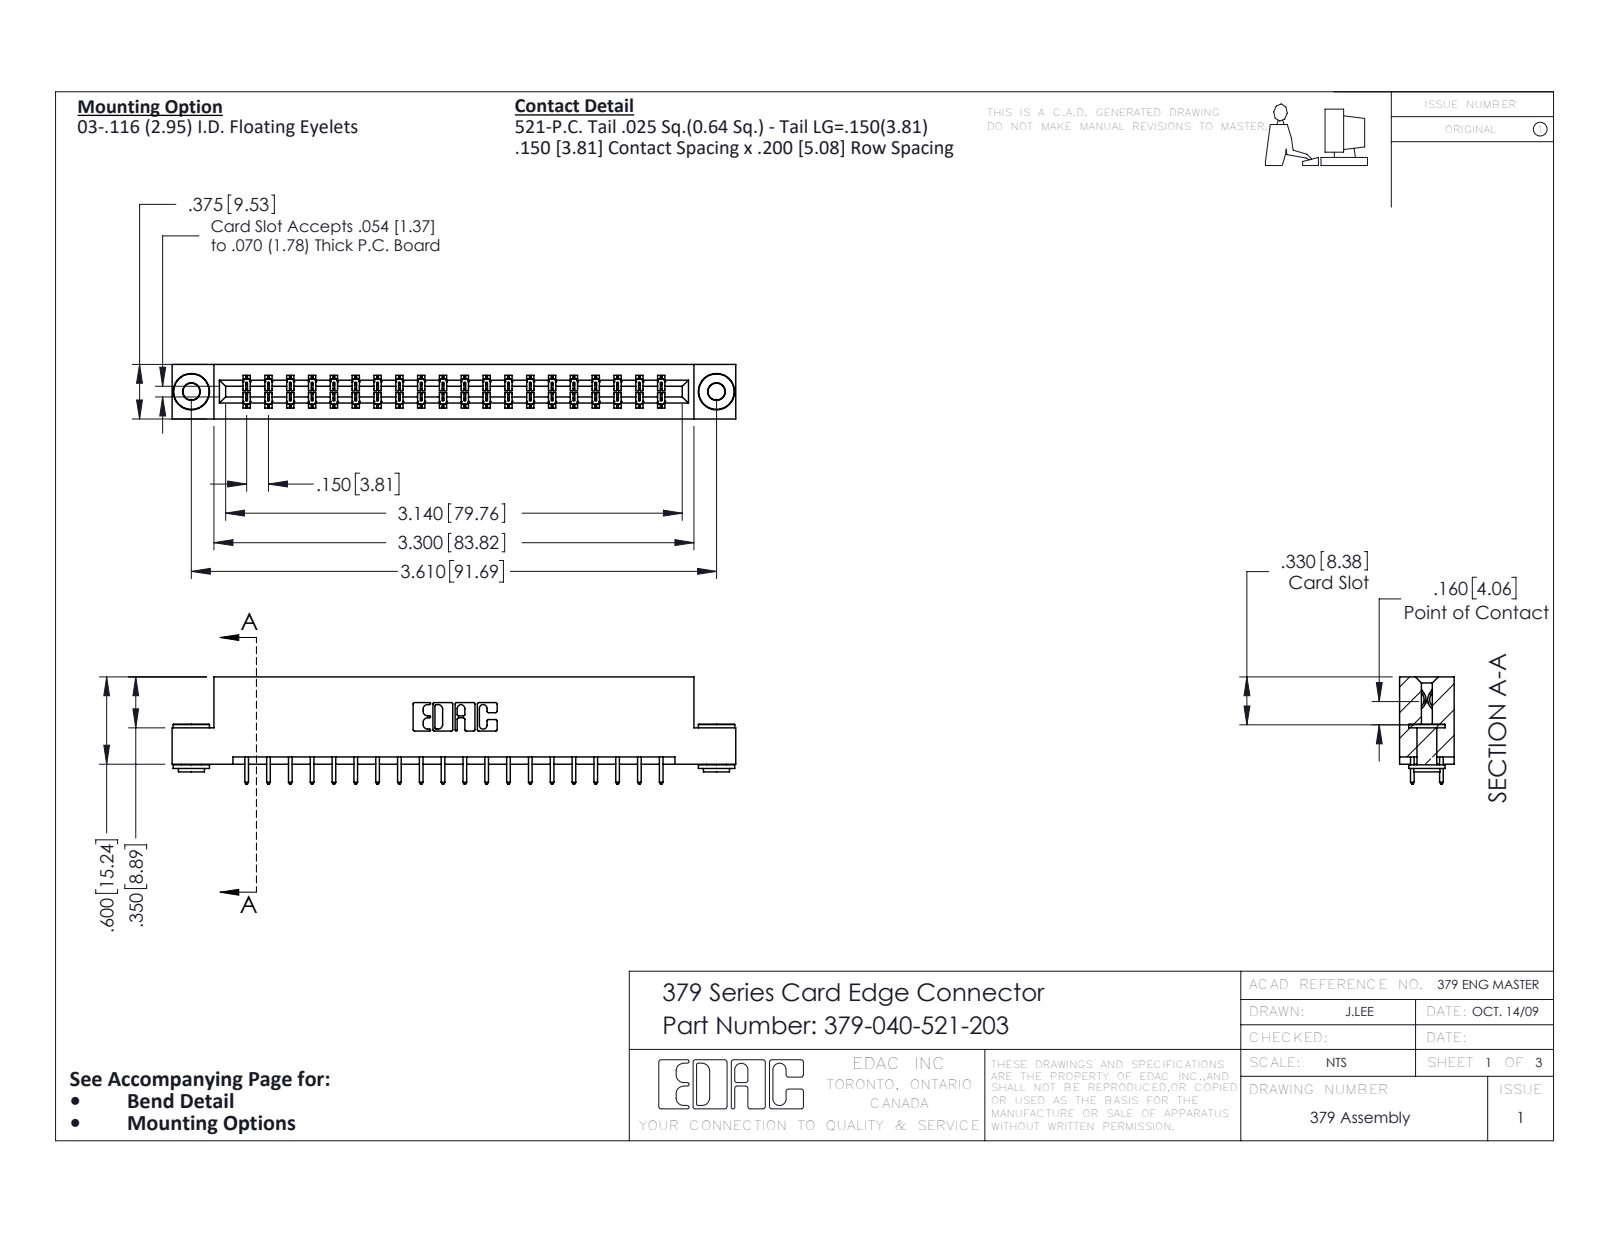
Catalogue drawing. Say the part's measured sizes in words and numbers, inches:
The part is named "379 Part_Flush - .156 Dia - TH; 379-040-521-203; 345-250-002_345-250-002-102; 345-292-001_345-293-121". Its 3-D file was written by "SolidWorks 2016 (CONFIG_CONTROL_DESIGN)". It is 43 solids with 2232 faces: 1520 planar, 704 cylindrical and 8 other. Overall it measures 3.875 by 0.737 by 0.375 inches. Its volume is 0.623 cubic inches and its surface area 17.63 square inches. Round holes: 2 of diameter 0.116, 2 of diameter 0.156. Round bosses or shafts: 2 of diameter 0.25, 2 of diameter 0.18, 2 of diameter 0.136. Partial cylindrical surfaces (rounded edges, fillets, slot ends): 60 of radius 0.006, 40 of radius 0.01, 22 of radius 0.01, 6 of radius 0.007, 6 of radius 0.031, 3 of radius 0.026, 2 of radius 0.014, 2 of radius 0.022. The main face-to-face distances are 0.3, 0.075, 0.375, 0.2, 0.1, 0.225, 0.275, 0.15, 0.05, 0.6. The hole center spacings are 3.61.
